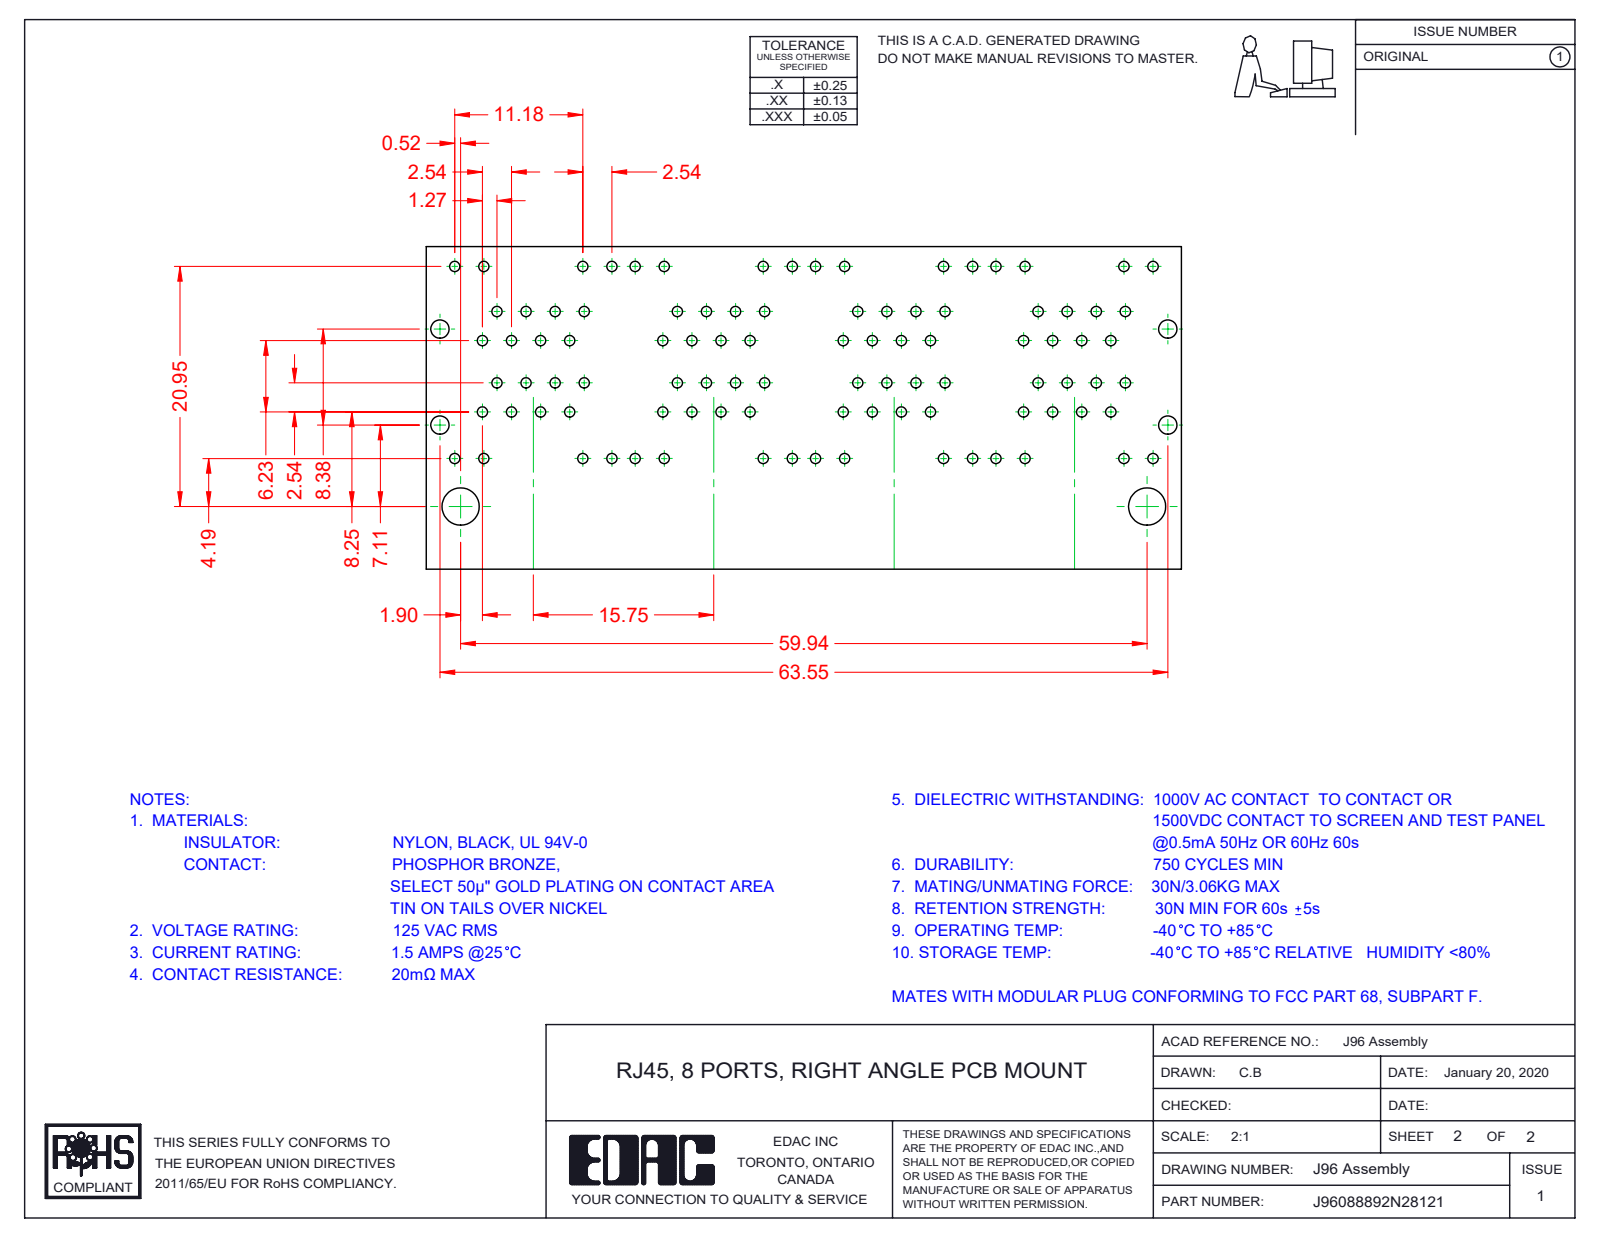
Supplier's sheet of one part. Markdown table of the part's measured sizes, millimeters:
| quantity | value |
| --- | --- |
| part name | J96088892N28121; 96 Insulator_8 Ports; 96 Back Plate_8 Ports; 96 LED RH Lower_8-Red-Yellow (+8 more) |
| STEP written by | SolidWorks 2016 (CONFIG_CONTROL_DESIGN) |
| units | millimeters |
| bodies | 96 solids, 7658 faces (6069 planar, 1323 cylindrical, 266 other) |
| overall size | 64.05 × 29.58 × 28.68 |
| volume | 24 160 mm³ |
| surface area | 63 658 mm² |
| round holes (diameter × count) | 1.7 × 3 |
| round bosses / shafts (diameter × count) | 1.68 × 3 |
| partial cylindrical surfaces (radius × count) | 0.25 × 124, 0.35 × 73, 1 × 72, 0.5 × 49, 0.91 × 32, 0.2 × 21, 0.7 × 11, 0.22 × 8 |
| main face-to-face distances | 15.75, 0.35, 9.95, 1.17, 1.6, 0.54, 9.98, 10.18, 12.67, 3.37 |
| hole center spacings | 15.75, 31.5 |
